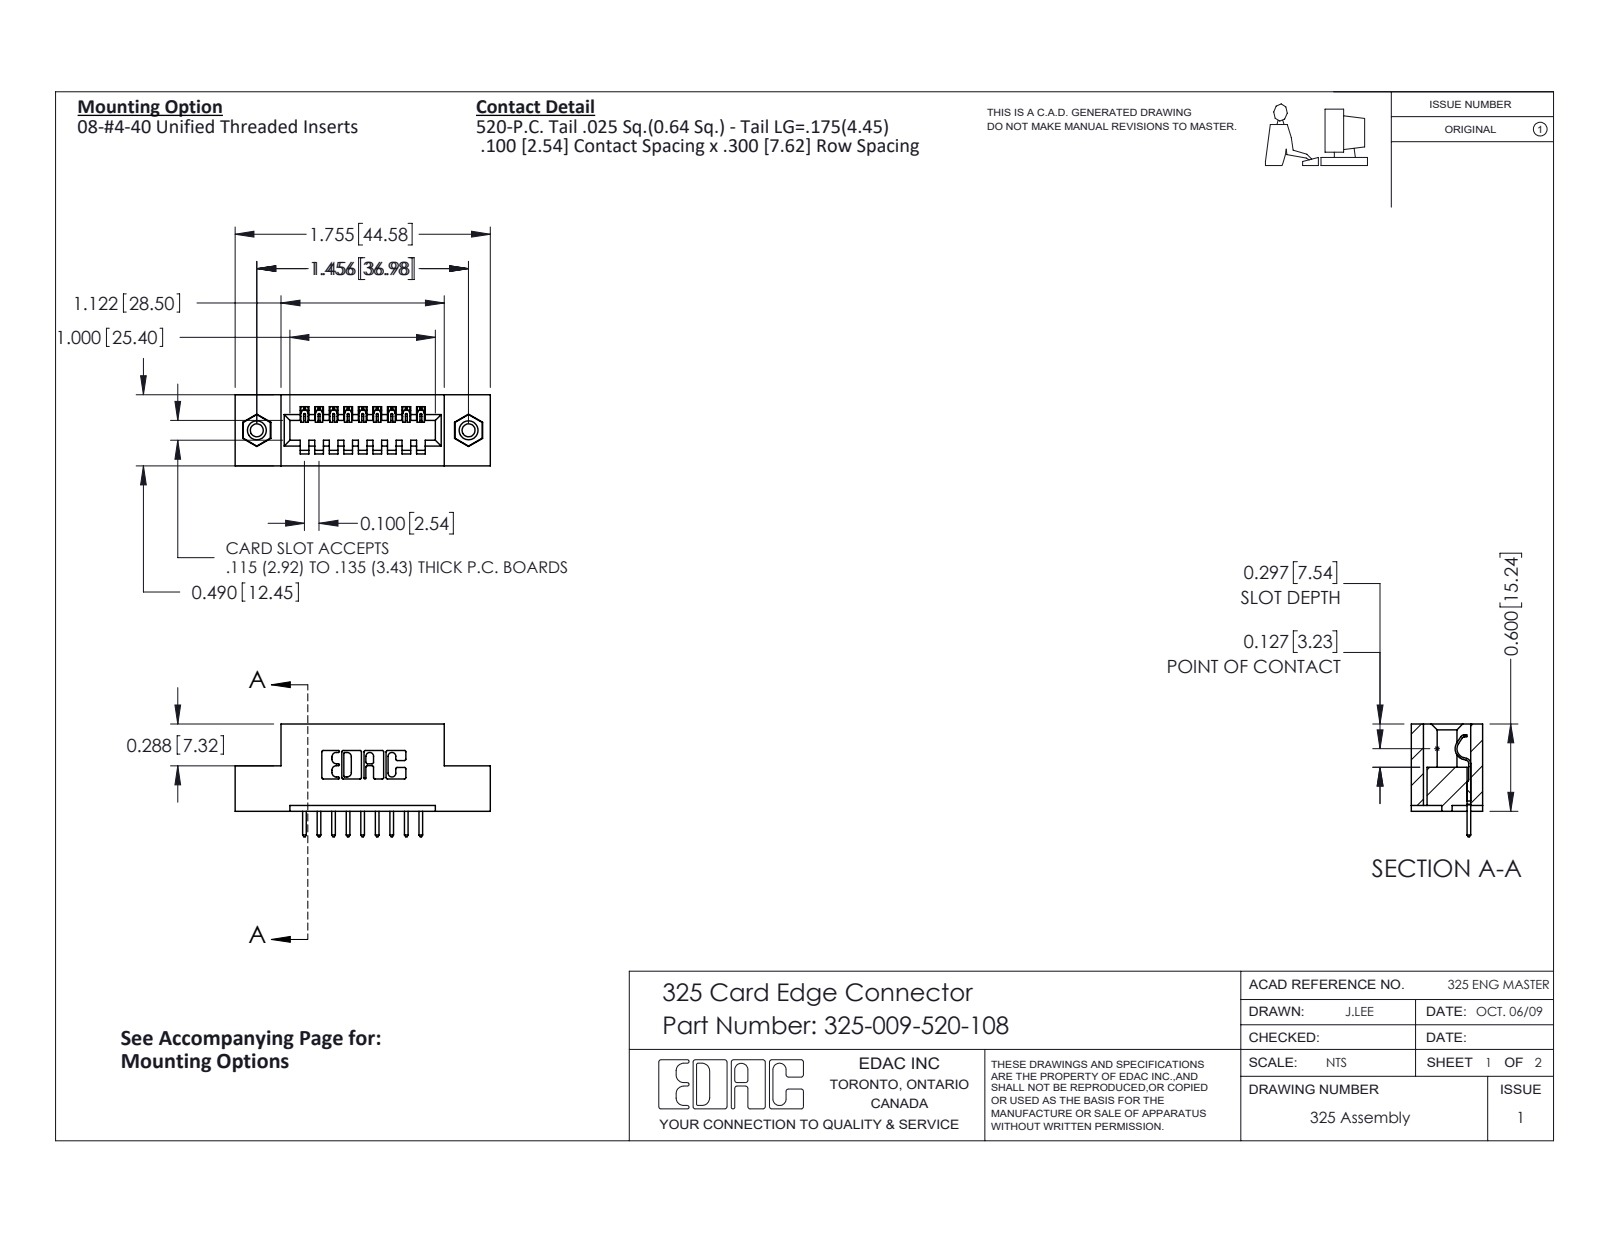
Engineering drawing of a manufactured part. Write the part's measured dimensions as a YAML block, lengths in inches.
part_name: "325-009-520-108; 325 Part_TI; 325-292-001_325-293-120; 345-250-001_345-250-003-102"
step_written_by: "SolidWorks 2016 (CONFIG_CONTROL_DESIGN)"
units: inches
bodies: {solids: 12, faces: 696, planar: 480, cylindrical: 200, other: 16}
overall_size: [1.755, 0.775, 0.49]
volume: 0.328
surface_area: 8.103
round_holes:
  - {diameter: 0.089, count: 2}
  - {diameter: 0.125, count: 2}
  - {diameter: 0.16, count: 2}
round_bosses_or_shafts:
  - {diameter: 0.155, count: 2}
partial_cylinders:
  - {radius: 0.01, count: 22}
  - {radius: 0.006, count: 18}
  - {radius: 0.01, count: 18}
  - {radius: 0.007, count: 6}
  - {radius: 0.031, count: 6}
  - {radius: 0.026, count: 3}
  - {radius: 0.014, count: 1}
  - {radius: 0.022, count: 1}
face_to_face_distances: [0.3, 0.04, 0.1, 0.083, 0.407, 0.49, 0.2, 0.6, 0.4, 0.06]
hole_center_spacings: [1.456]
